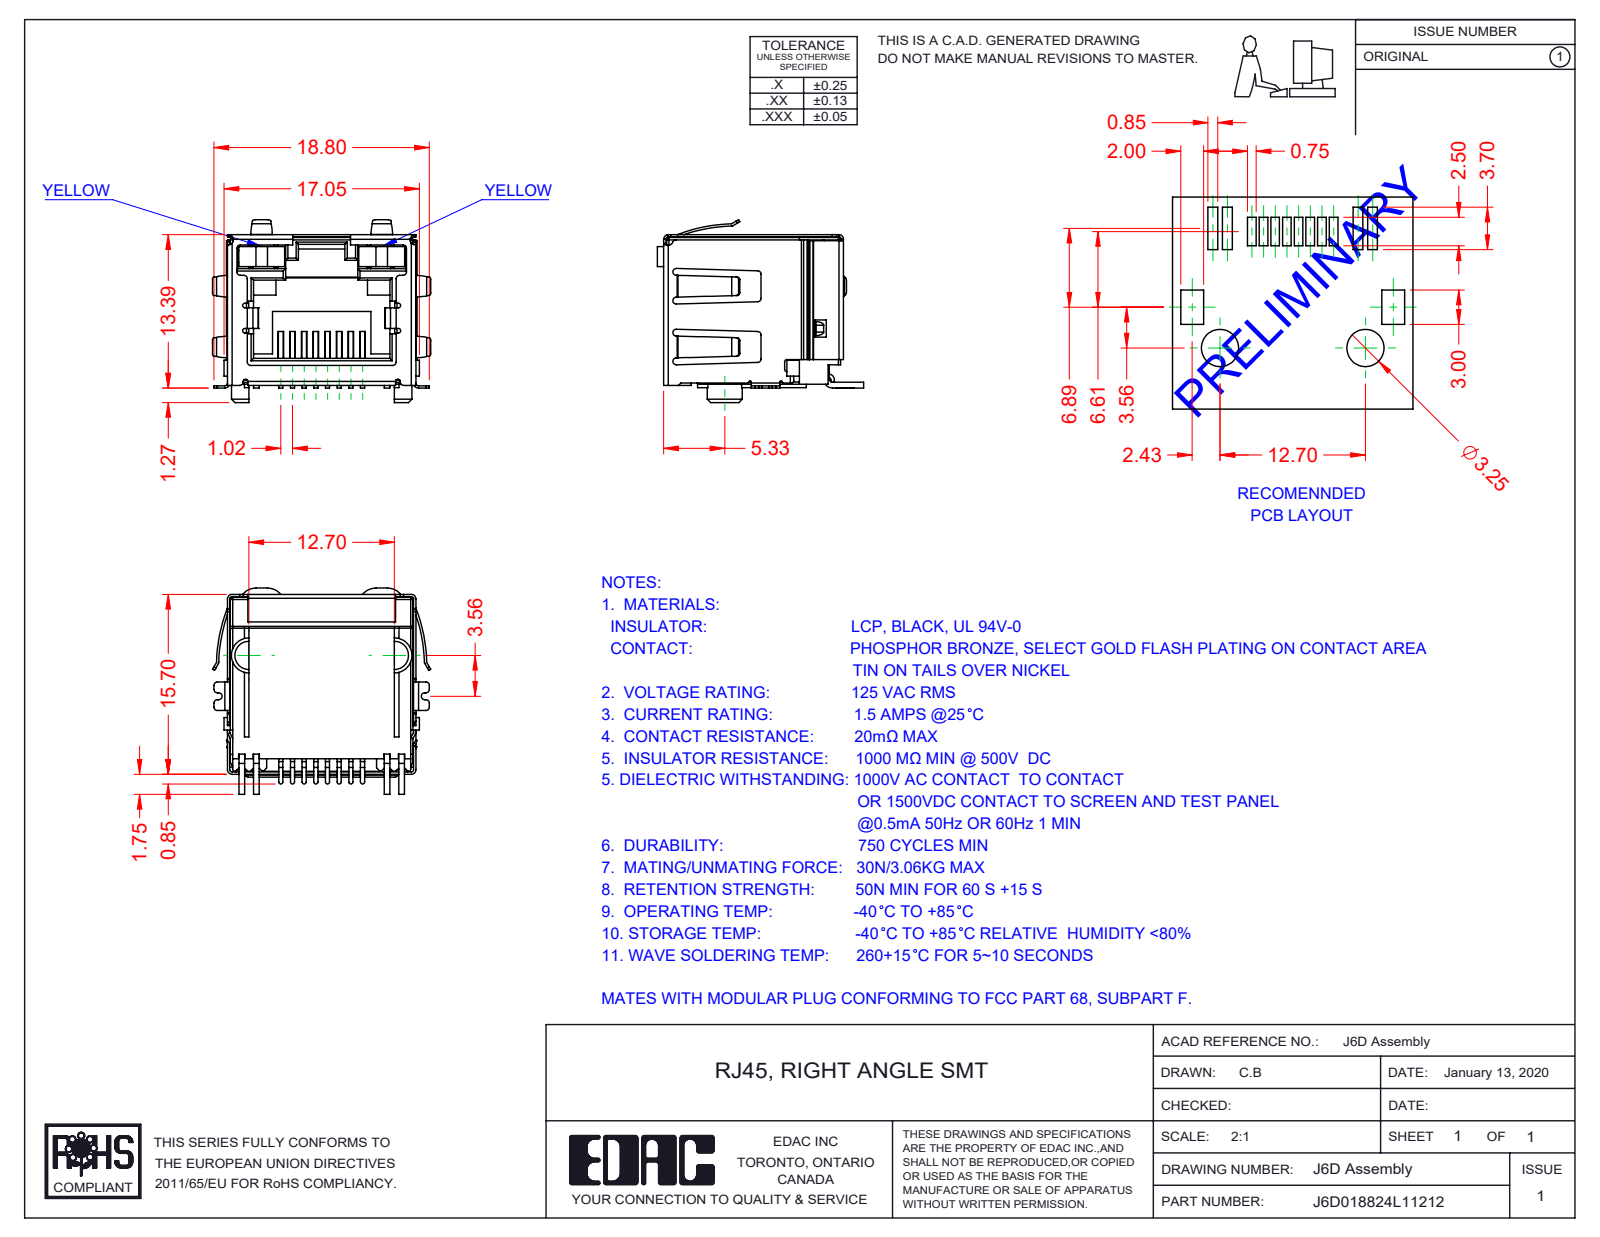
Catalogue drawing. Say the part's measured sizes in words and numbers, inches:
The part is named "6D LED LH_1-Yellow; 6D Contacts; 6D Insulator; J6D018824L11212 (+2 more)". Its 3-D file was written by "SolidWorks 2016 (CONFIG_CONTROL_DESIGN)". It is 12 solids with 1028 faces: 701 planar, 282 cylindrical and 45 other. Overall it measures 0.75 by 0.709 by 0.628 inches. Its volume is 0.109 cubic inches and its surface area 7.434 square inches. Partial cylindrical surfaces (rounded edges, fillets, slot ends): 55 of radius 0.012, 40 of radius 0.008, 19 of radius 0.016, 16 of radius 0.01, 12 of radius 0.004, 8 of radius 0.006, 8 of radius 0.007, 6 of radius 0.02. The main face-to-face distances are 0.63, 0.638, 0.64, 0.089, 0.039, 0.628, 0.504, 0.018, 0.514, 0.417.
